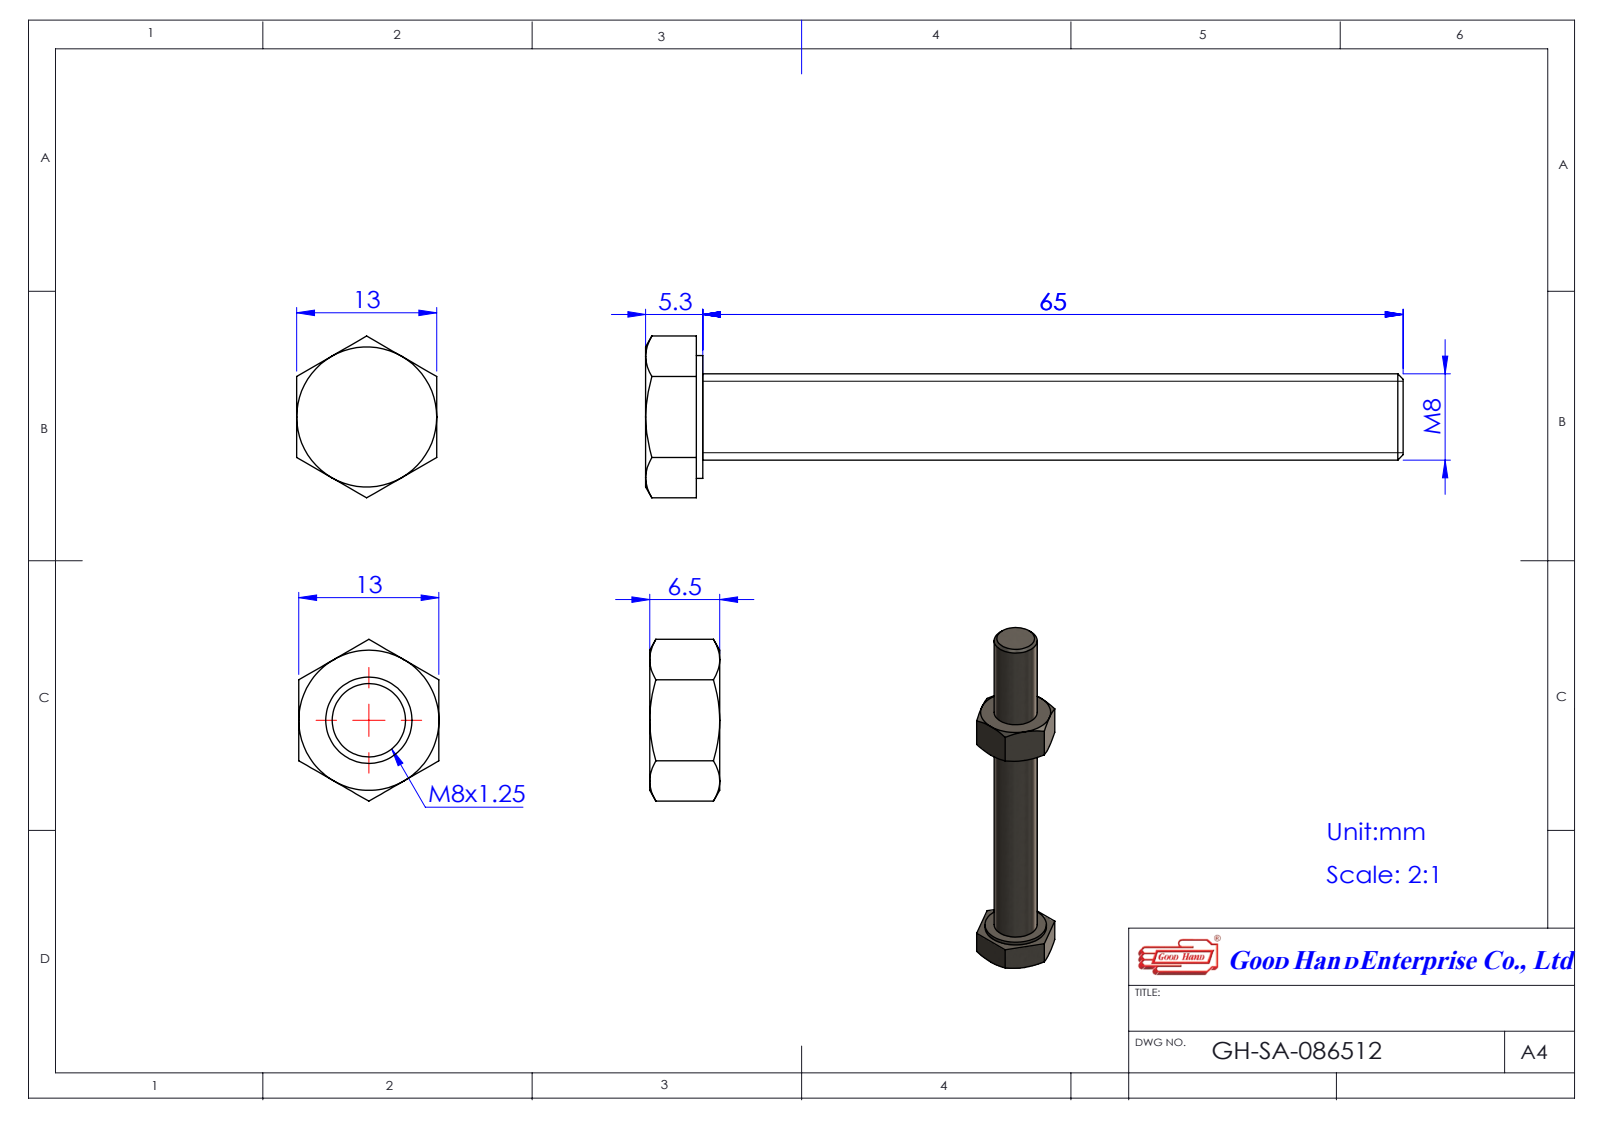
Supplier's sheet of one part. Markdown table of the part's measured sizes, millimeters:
| quantity | value |
| --- | --- |
| part name | SA-086512; 6200080K(DIN934_JIS_)_B18.2.4.1M - Hex nut, Style 1, M8 x 1.25 --D-N |
| STEP written by | SolidWorks 2016 (AUTOMOTIVE_DESIGN) |
| units | millimeters |
| bodies | 2 solids, 48 faces (18 planar, 8 cylindrical, 22 other) |
| overall size | 70.3 × 15.01 × 13 |
| volume | 4 718 mm³ |
| surface area | 2 779 mm² |
| round holes (diameter × count) | 6.8 × 1, 8 × 1 |
| round bosses / shafts (diameter × count) | 11.4 × 1 |
| main face-to-face distances | 13, 53.52, 47.02, 6.5, 5.3, 41.72, 48.22, 70.3, 65, 23.28 |
